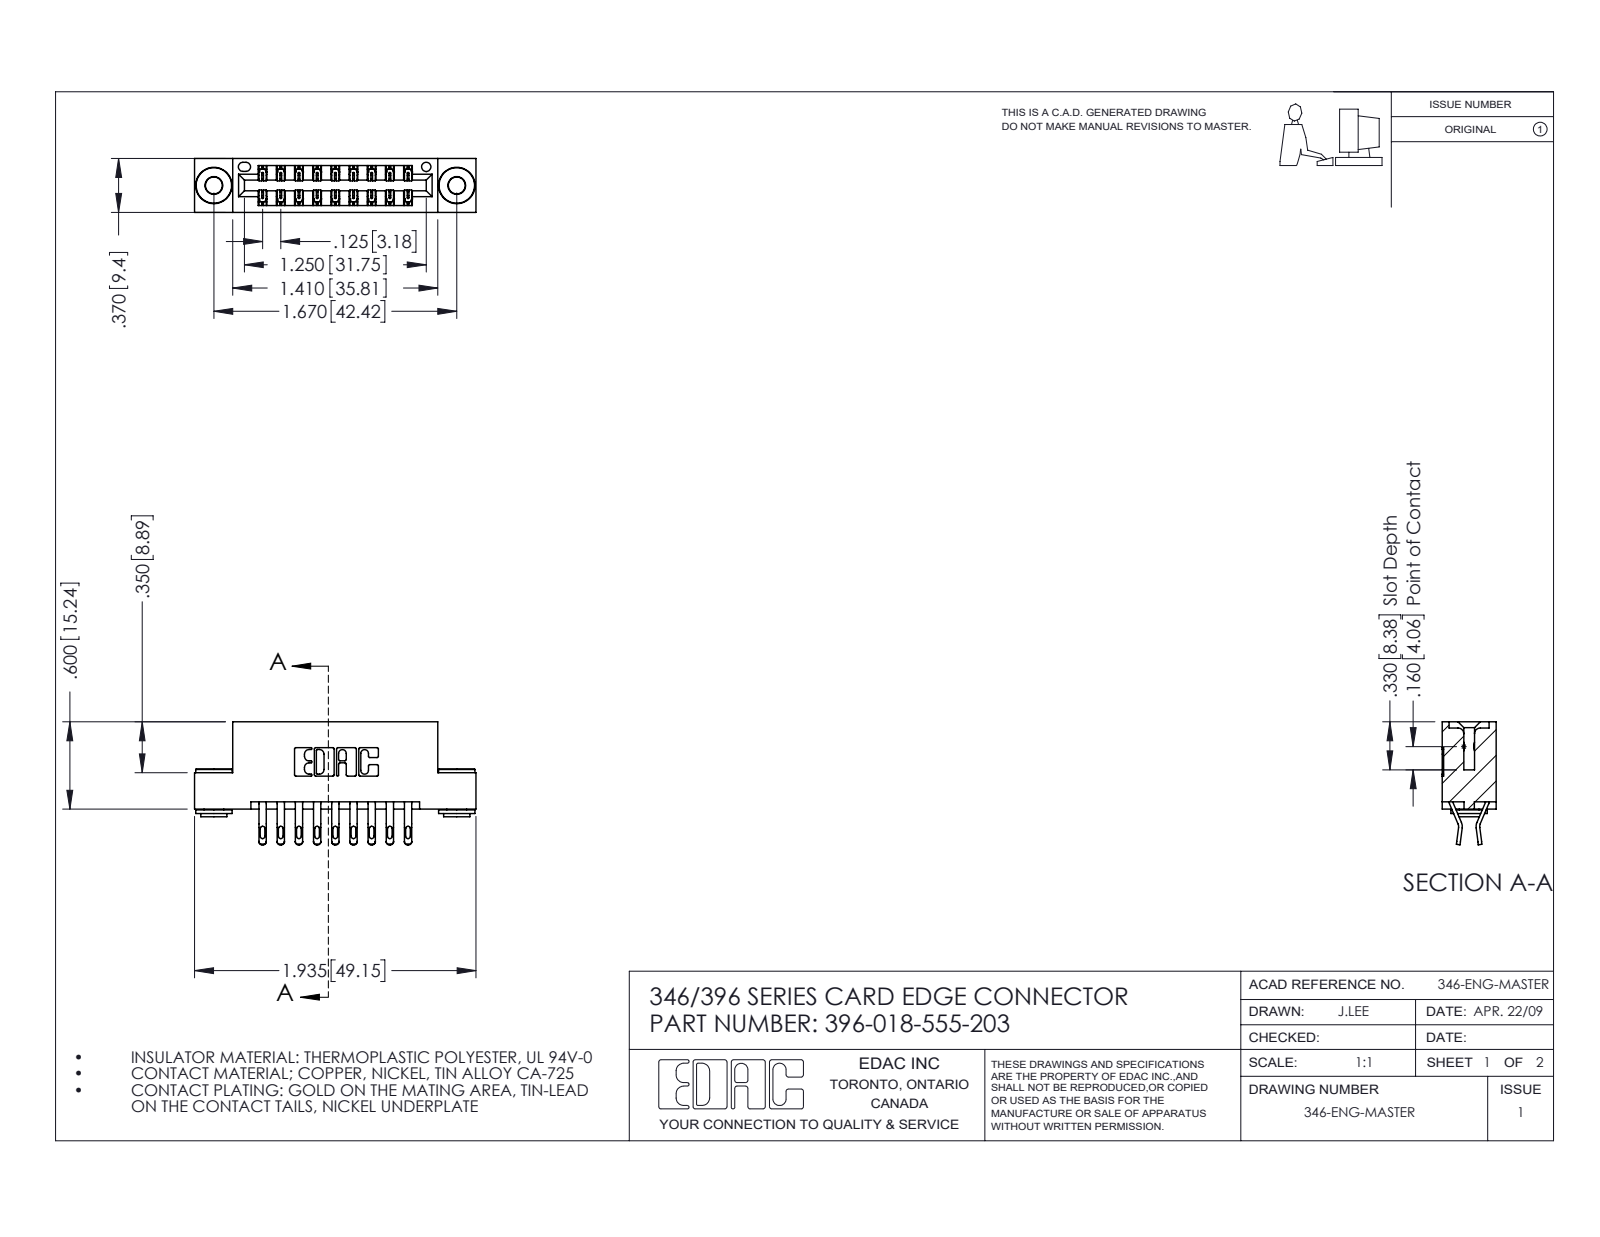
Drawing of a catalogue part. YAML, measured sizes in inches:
part_name: "346 Part_Flush Mounting Lugs - 0.156 Dia-TH; 396-018-555-203; 345-250-002_345-250-002-102; 345-292-001_555 Tail"
step_written_by: "SolidWorks 2016 (CONFIG_CONTROL_DESIGN)"
units: inches
bodies: {solids: 21, faces: 1204, planar: 680, cylindrical: 516, other: 8}
overall_size: [1.935, 0.845, 0.37]
volume: 0.281
surface_area: 9.634
round_holes:
  - {diameter: 0.116, count: 2}
  - {diameter: 0.156, count: 2}
  - {diameter: 0.064, count: 1}
round_bosses_or_shafts:
  - {diameter: 0.25, count: 2}
  - {diameter: 0.18, count: 2}
  - {diameter: 0.136, count: 2}
partial_cylinders:
  - {radius: 0.016, count: 36}
  - {radius: 0.02, count: 36}
  - {radius: 0.006, count: 27}
  - {radius: 0.01, count: 22}
  - {radius: 0.007, count: 6}
  - {radius: 0.031, count: 6}
  - {radius: 0.026, count: 3}
  - {radius: 0.01, count: 2}
face_to_face_distances: [0.25, 0.048, 0.322, 0.37, 0.025, 0.148, 0.072, 0.298, 0.222, 0.1]
hole_center_spacings: [0.246, 1.465, 1.67]
